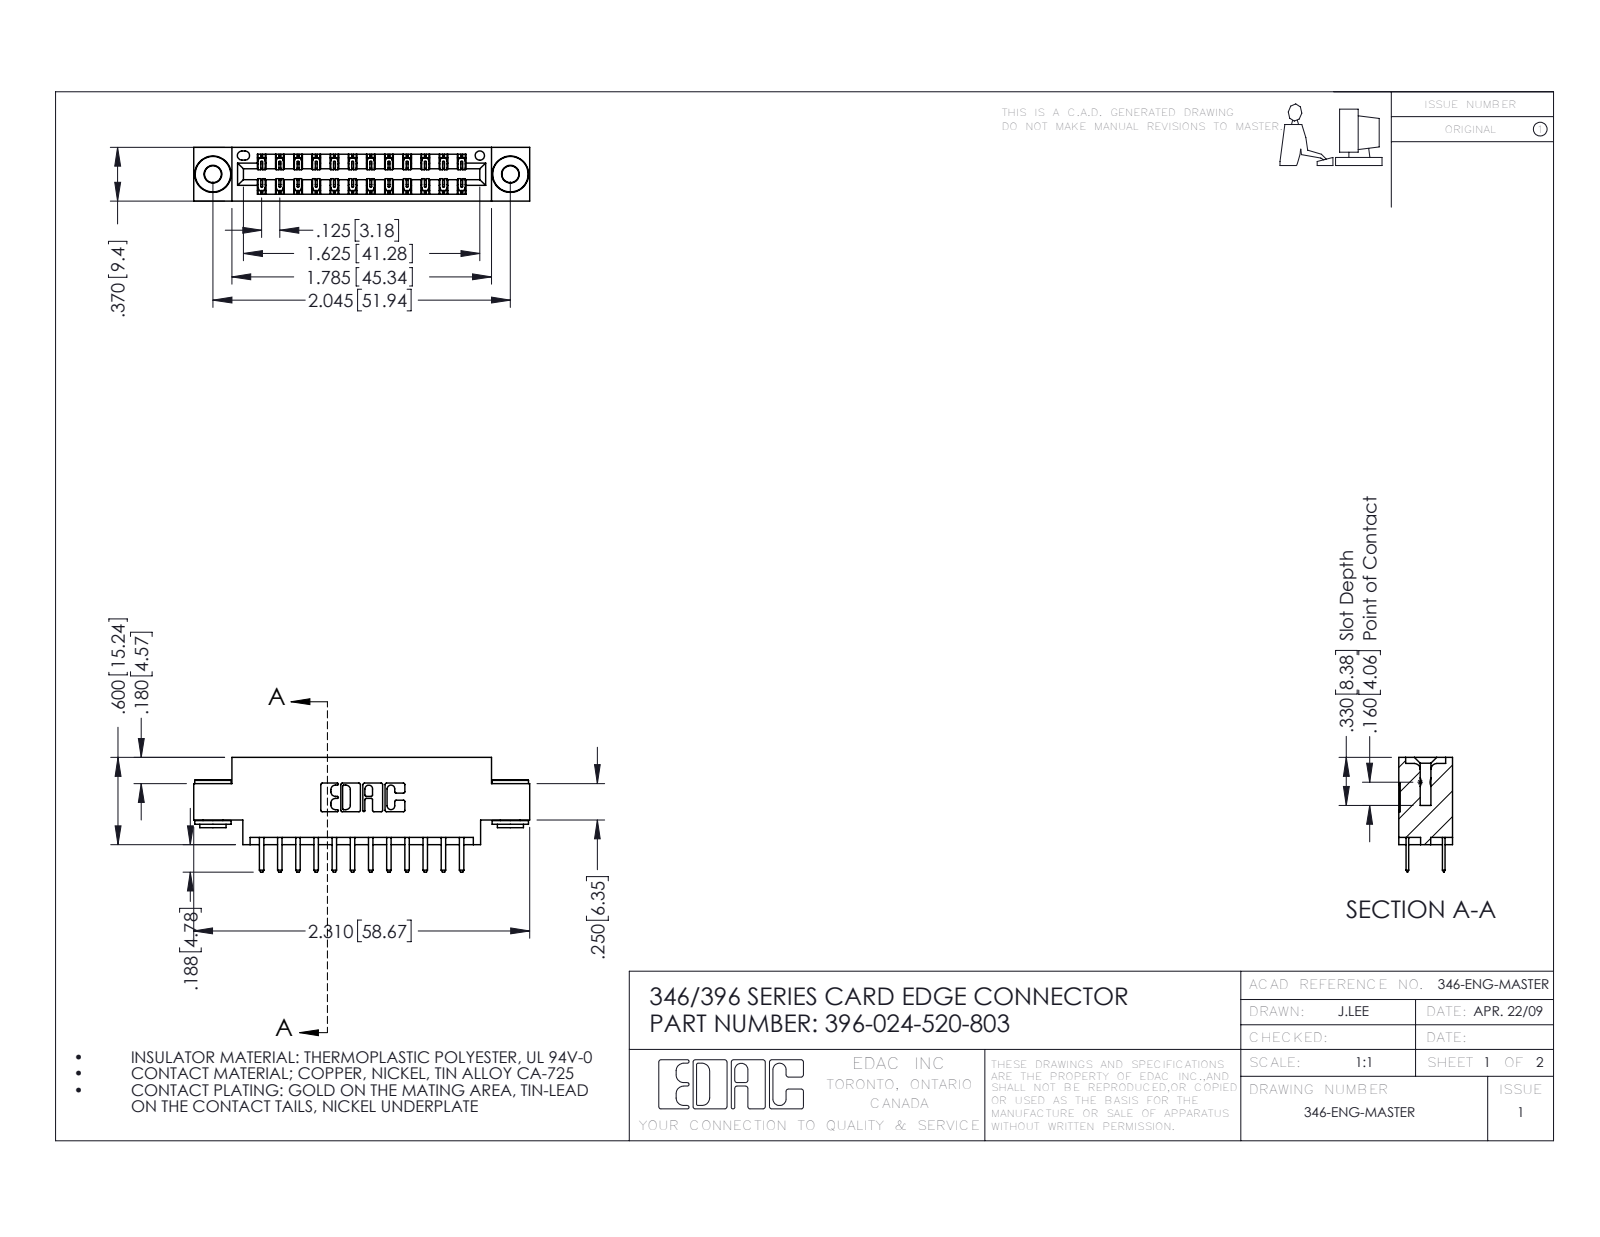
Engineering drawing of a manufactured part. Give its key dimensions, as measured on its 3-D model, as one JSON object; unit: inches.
{"part_name": "345-250-002_345-250-002-102; 345-292-001_345-293-120; 346 Part_0.170 Offset - 0.156 Dia-TH; 396-024-520-803", "step_written_by": "SolidWorks 2016 (CONFIG_CONTROL_DESIGN)", "units": "inches", "bodies": {"solids": 27, "faces": 1508, "planar": 978, "cylindrical": 522, "other": 8}, "overall_size": [2.31, 0.788, 0.37], "volume_in3": 0.326, "surface_area_in2": 11.22, "round_holes": [[0.116, 2], [0.156, 2], [0.064, 1]], "round_bosses_or_shafts": [[0.25, 2], [0.18, 2], [0.136, 2]], "partial_cylinders_radius": [[0.006, 36], [0.01, 28], [0.01, 22], [0.007, 6], [0.031, 6], [0.026, 3], [0.014, 2], [0.022, 2]], "face_to_face_distances": [0.25, 0.37, 0.048, 0.322, 0.025, 0.275, 0.148, 0.222, 0.1, 0.174], "hole_center_spacings": [0.246, 1.839, 2.045]}
